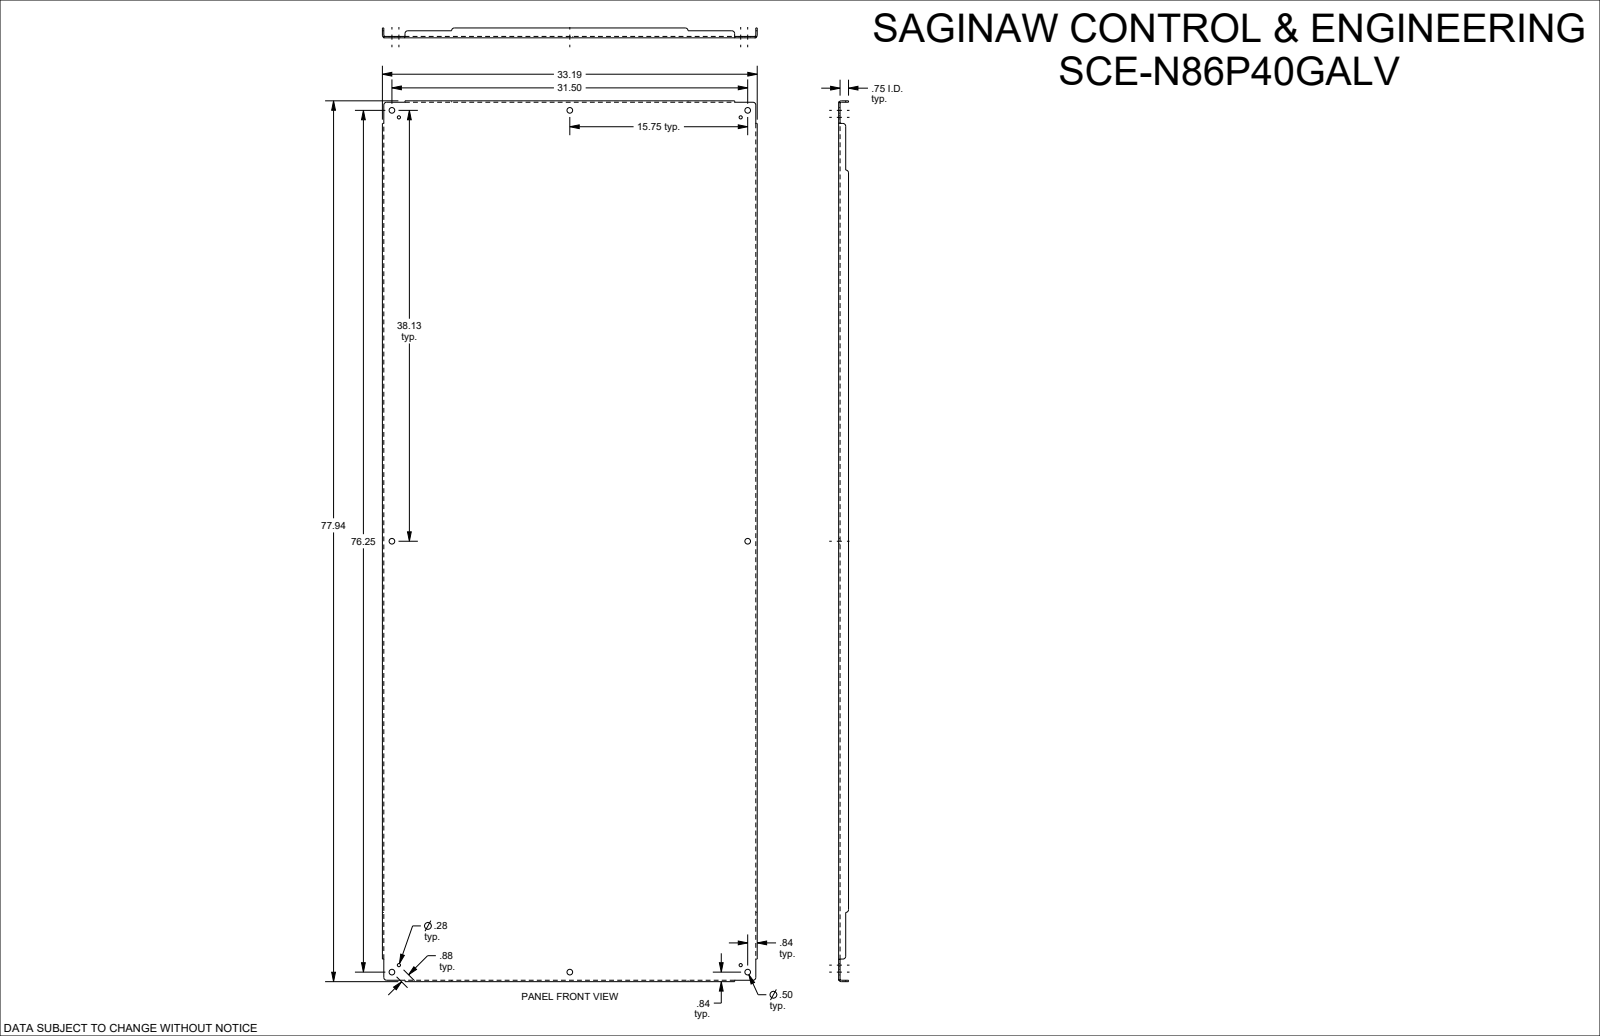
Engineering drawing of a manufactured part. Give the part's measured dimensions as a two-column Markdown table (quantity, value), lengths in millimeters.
| quantity | value |
| --- | --- |
| part name | SCE-N86P40GALV |
| STEP written by | SolidWorks 2023 (AUTOMOTIVE_DESIGN) |
| units | millimeters |
| bodies | 1 solid, 122 faces (46 planar, 52 cylindrical, 24 other) |
| overall size | 1979.6 × 843 × 22.2 |
| volume | 5 558 000 mm³ |
| surface area | 3 521 000 mm² |
| round holes (diameter × count) | 12.7 × 8, 7.1 × 4 |
| partial cylindrical surfaces (radius × count) | 6.4 × 12, 2.8 × 4, 6 × 4 |
| main face-to-face distances | 3.2, 839.8, 836.6, 842.9, 3.2, 1976.5, 19.1, 22.2, 1973.2, 1979.6 |
| hole center spacings | 22.2, 384.7, 400.1, 784.5, 952.8, 968.4, 1047.8, 1234 |
